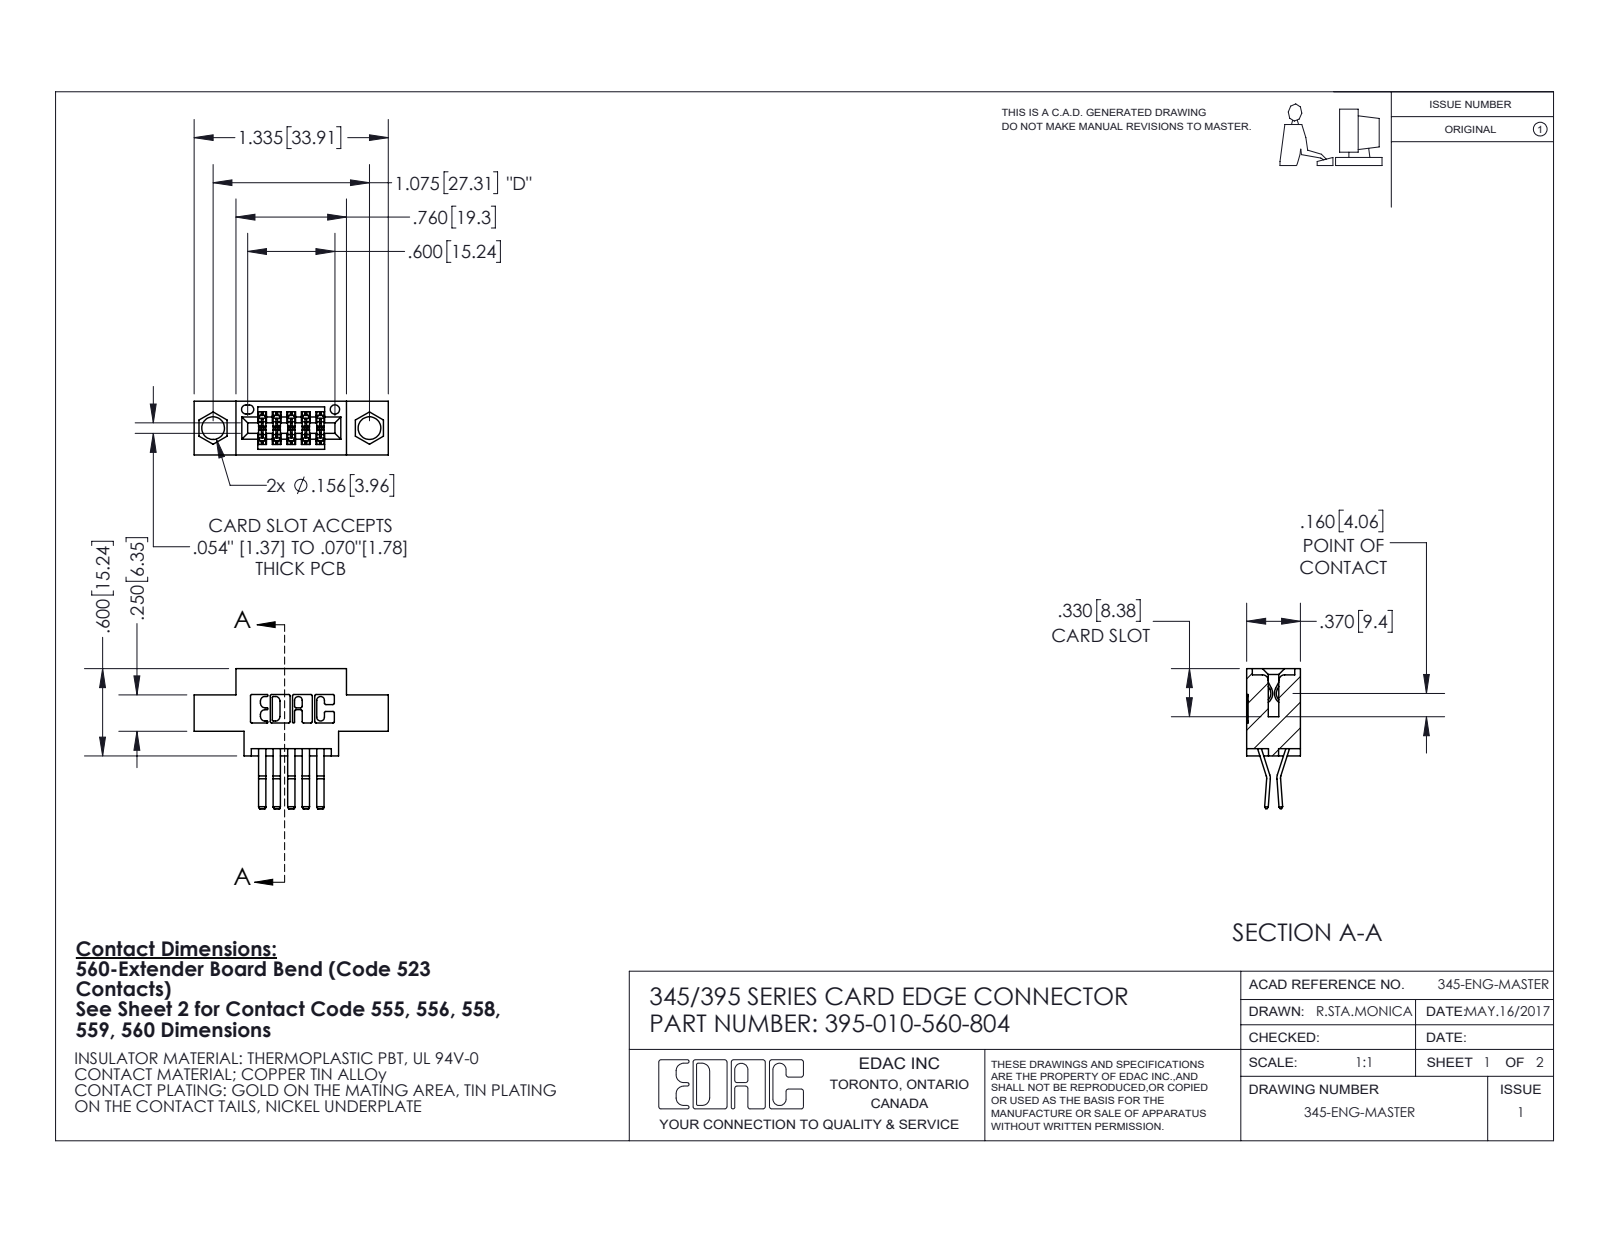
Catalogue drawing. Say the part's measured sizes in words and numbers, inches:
The part is named "345-292-001_560 Tail; 345 Part_0.170 Offset - 0.156 Dia-TI; 395-010-560-804". Its 3-D file was written by "SolidWorks 2020 (CONFIG_CONTROL_DESIGN)". It is 11 solids with 664 faces: 428 planar, 236 cylindrical and 0 other. Overall it measures 1.335 by 0.962 by 0.37 inches. Its volume is 0.171 cubic inches and its surface area 5.551 square inches. Round holes: 2 of diameter 0.156, 1 of diameter 0.064. Partial cylindrical surfaces (rounded edges, fillets, slot ends): 22 of radius 0.01, 15 of radius 0.006, 6 of radius 0.007, 6 of radius 0.031, 3 of radius 0.026, 2 of radius 0.01, 2 of radius 0.014, 2 of radius 0.019. The main face-to-face distances are 0.37, 0.2, 0.1, 0.025, 0.298, 0.072, 0.25, 0.15, 0.055, 0.098. The hole center spacings are 0.27, 0.847, 1.075.
